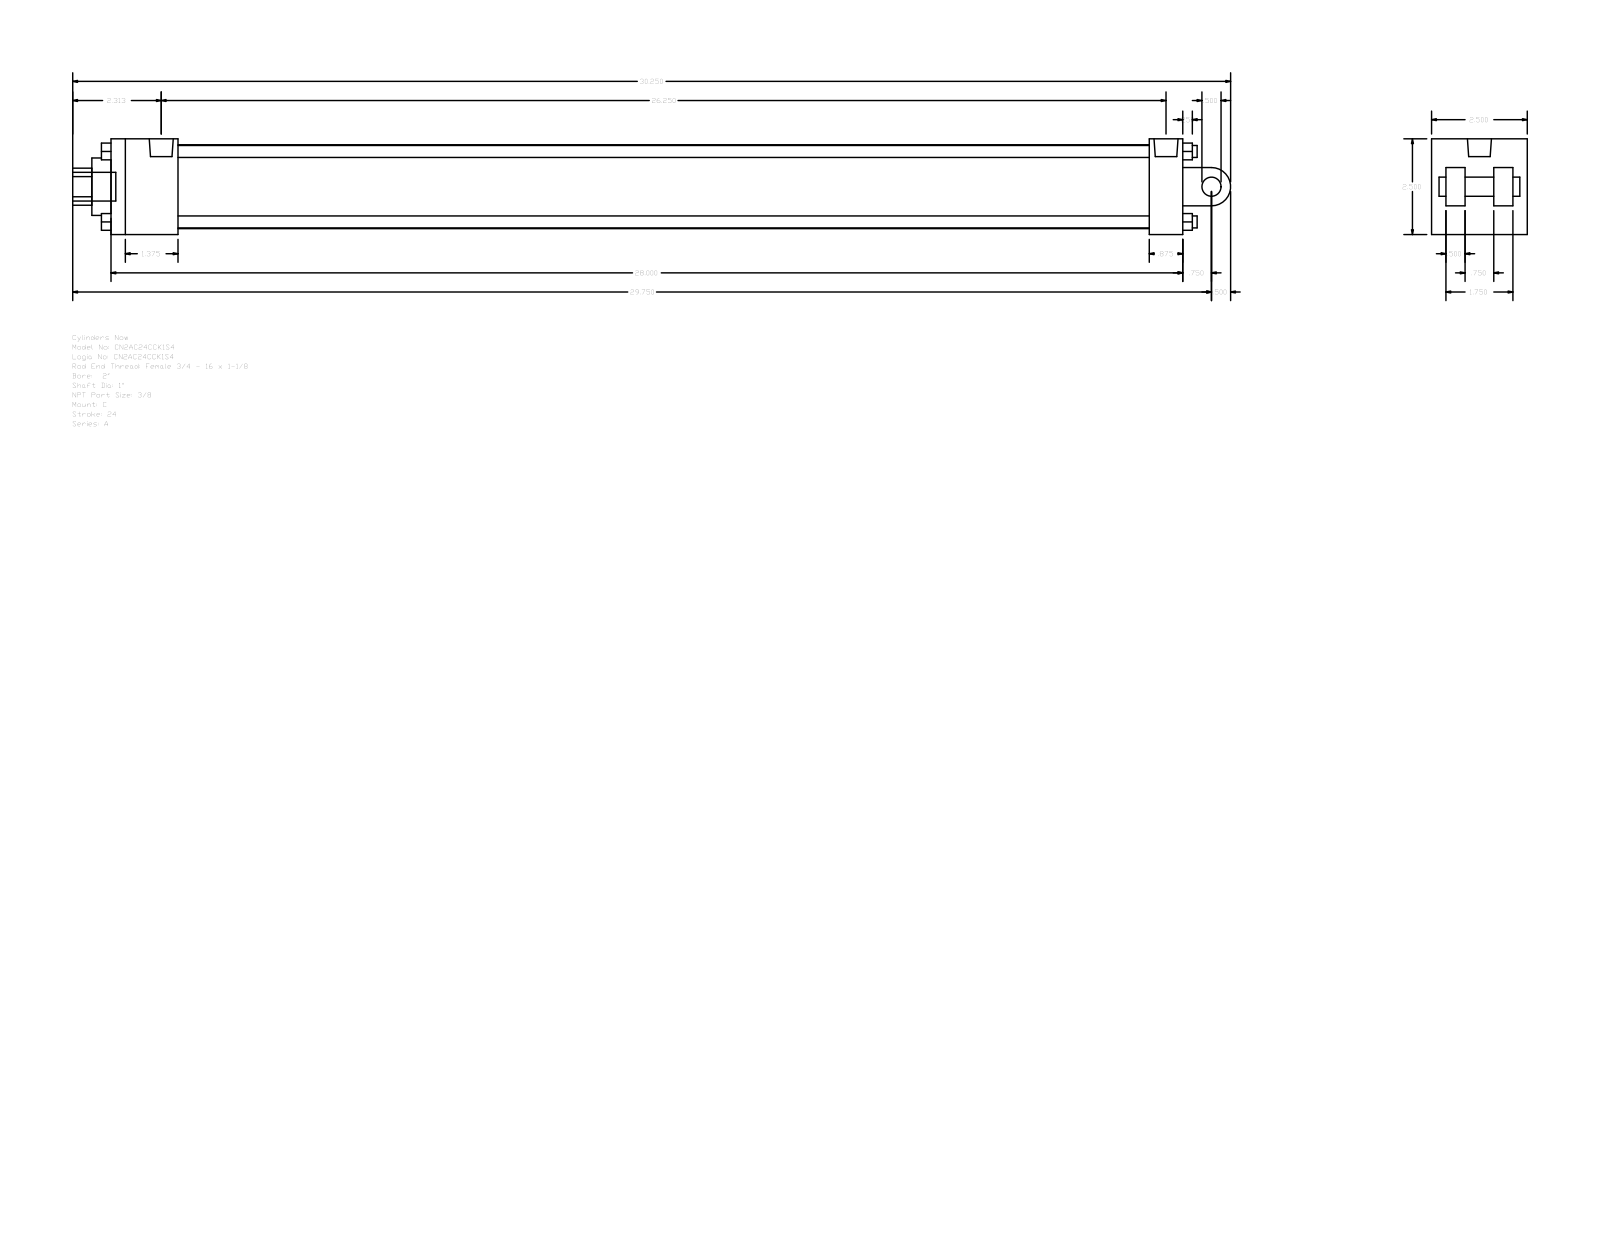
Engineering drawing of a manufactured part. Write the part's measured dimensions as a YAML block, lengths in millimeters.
part_name: "A_C__0200_1"
step_written_by: "GSSL Pune (CONFIG_CONTROL_DESIGN)"
units: millimeters
bodies: {solids: 0, faces: 135, planar: 102, cylindrical: 33, other: 0}
overall_size: [768.35, 63.5, 63.5]
round_holes:
  - {diameter: 5.56, count: 2}
  - {diameter: 15.93, count: 1}
  - {diameter: 25.4, count: 1}
  - {diameter: 38.1, count: 1}
  - {diameter: 55.63, count: 1}
round_bosses_or_shafts:
  - {diameter: 7.94, count: 4}
  - {diameter: 5.56, count: 2}
  - {diameter: 19.05, count: 1}
  - {diameter: 15.93, count: 1}
  - {diameter: 12.7, count: 1}
partial_cylinders:
  - {radius: 12.29, count: 1}
  - {radius: 12.7, count: 1}
face_to_face_distances: [63.5, 22.22, 711.2, 44.45, 12.7, 9.52, 41.28, 666.75, 688.98, 644.53]
hole_center_spacings: [3.98]
